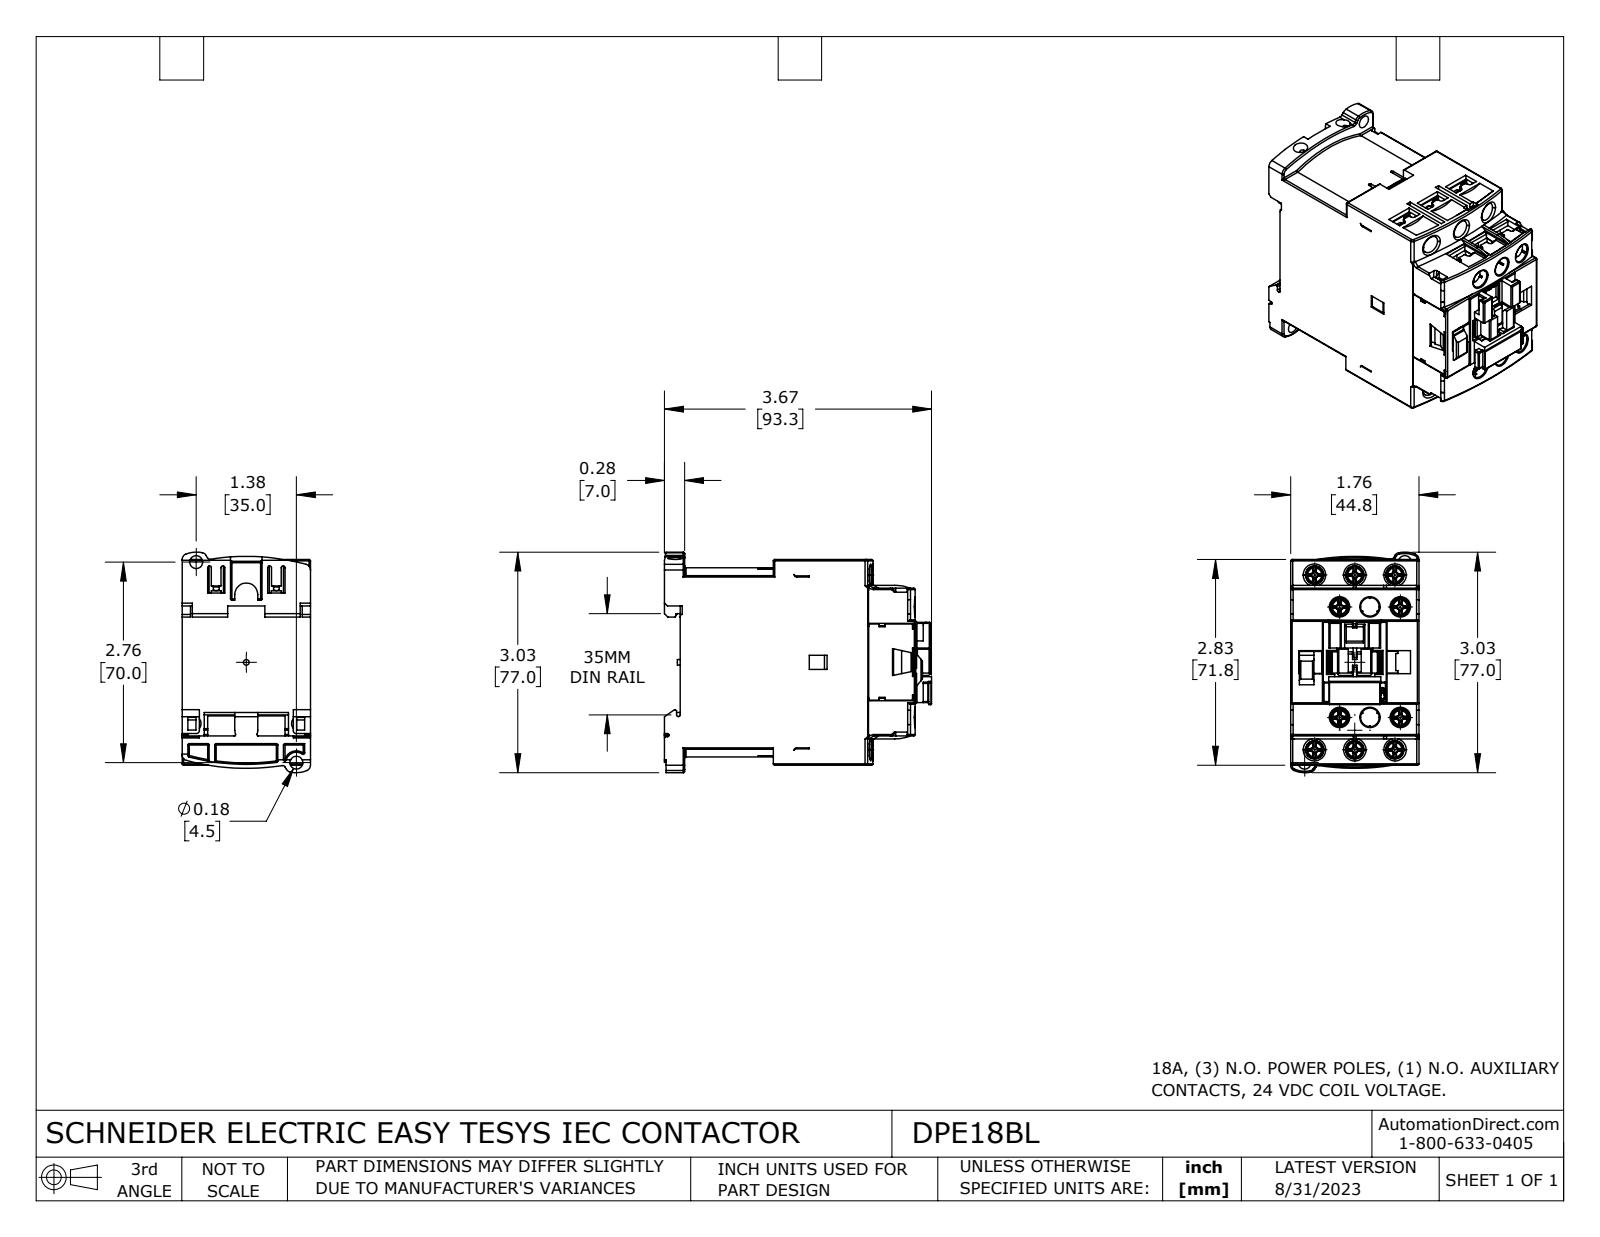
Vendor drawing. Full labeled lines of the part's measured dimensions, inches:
Part name (STEP PRODUCT): DPE18BL
STEP written by: SolidWorks 2021 (CONFIG_CONTROL_DESIGN)
Units: inches
Bodies: 10 solids, 3575 faces (2470 planar, 705 cylindrical, 400 other)
Overall size (bounding box): 3.671 × 3.031 × 1.764
Volume: 12.53 in³ · Surface area: 94.96 in²
Round holes (diameter × count): ⌀0.252 ×6, ⌀0.256 ×6, ⌀0.039 ×2, ⌀0.177 ×2, ⌀0.197 ×2, ⌀0.098 ×1, ⌀0.167 ×1, ⌀0.236 ×1
Round bosses / shafts (diameter × count): ⌀0.138 ×10, ⌀0.108 ×10, ⌀0.315 ×6, ⌀0.157 ×2, ⌀0.079 ×1
Partial cylindrical surfaces — rounded edges, fillets, slot ends (radius × count): R0.02 ×91, R0.006 ×42, R0.039 ×34, R0.012 ×31, R0.016 ×22, R0.008 ×14, R0.031 ×10, R0.157 ×9
Main face-to-face distances: 1.764, 0.272, 2.579, 2.555, 0.047, 0.217, 0.15, 2.283, 1.717, 0.173
Hole centre spacings: 0.417, 0.551, 1.576, 2.464, 1.52, 2.402, 0.224, 0.274
